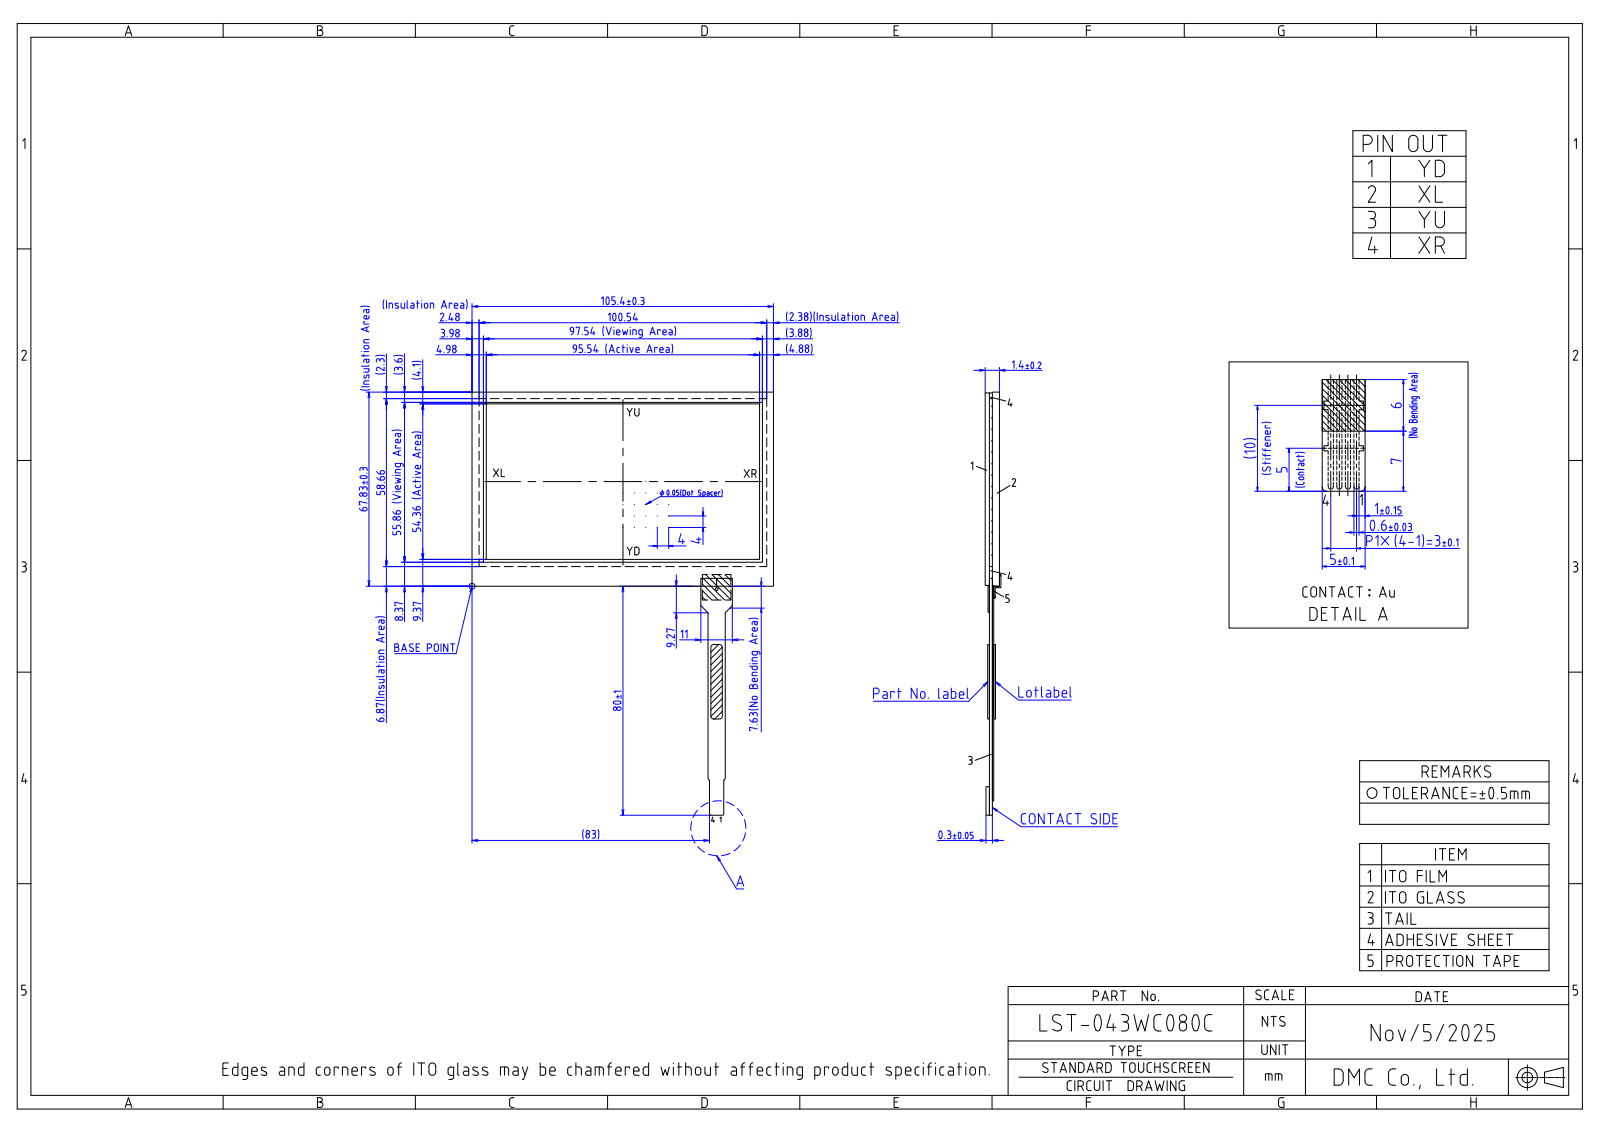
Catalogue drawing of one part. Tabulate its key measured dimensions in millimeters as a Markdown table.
| quantity | value |
| --- | --- |
| part name | LST-043WC080C-2 |
| STEP written by | Autodesk Inventor 2020 (CONFIG_CONTROL_DESIGN) |
| units | millimeters |
| bodies | 1 solid, 59 faces (45 planar, 14 cylindrical, 0 other) |
| overall size | 147.83 × 105.4 × 1.5 |
| volume | 10 047 mm³ |
| surface area | 15 886 mm² |
| partial cylindrical surfaces (radius × count) | 0.5 × 10, 0.3 × 4 |
| main face-to-face distances | 1.4, 1.1, 1.2, 1.3, 67.83, 105.4, 0.4, 1.5, 1, 0.5 |
